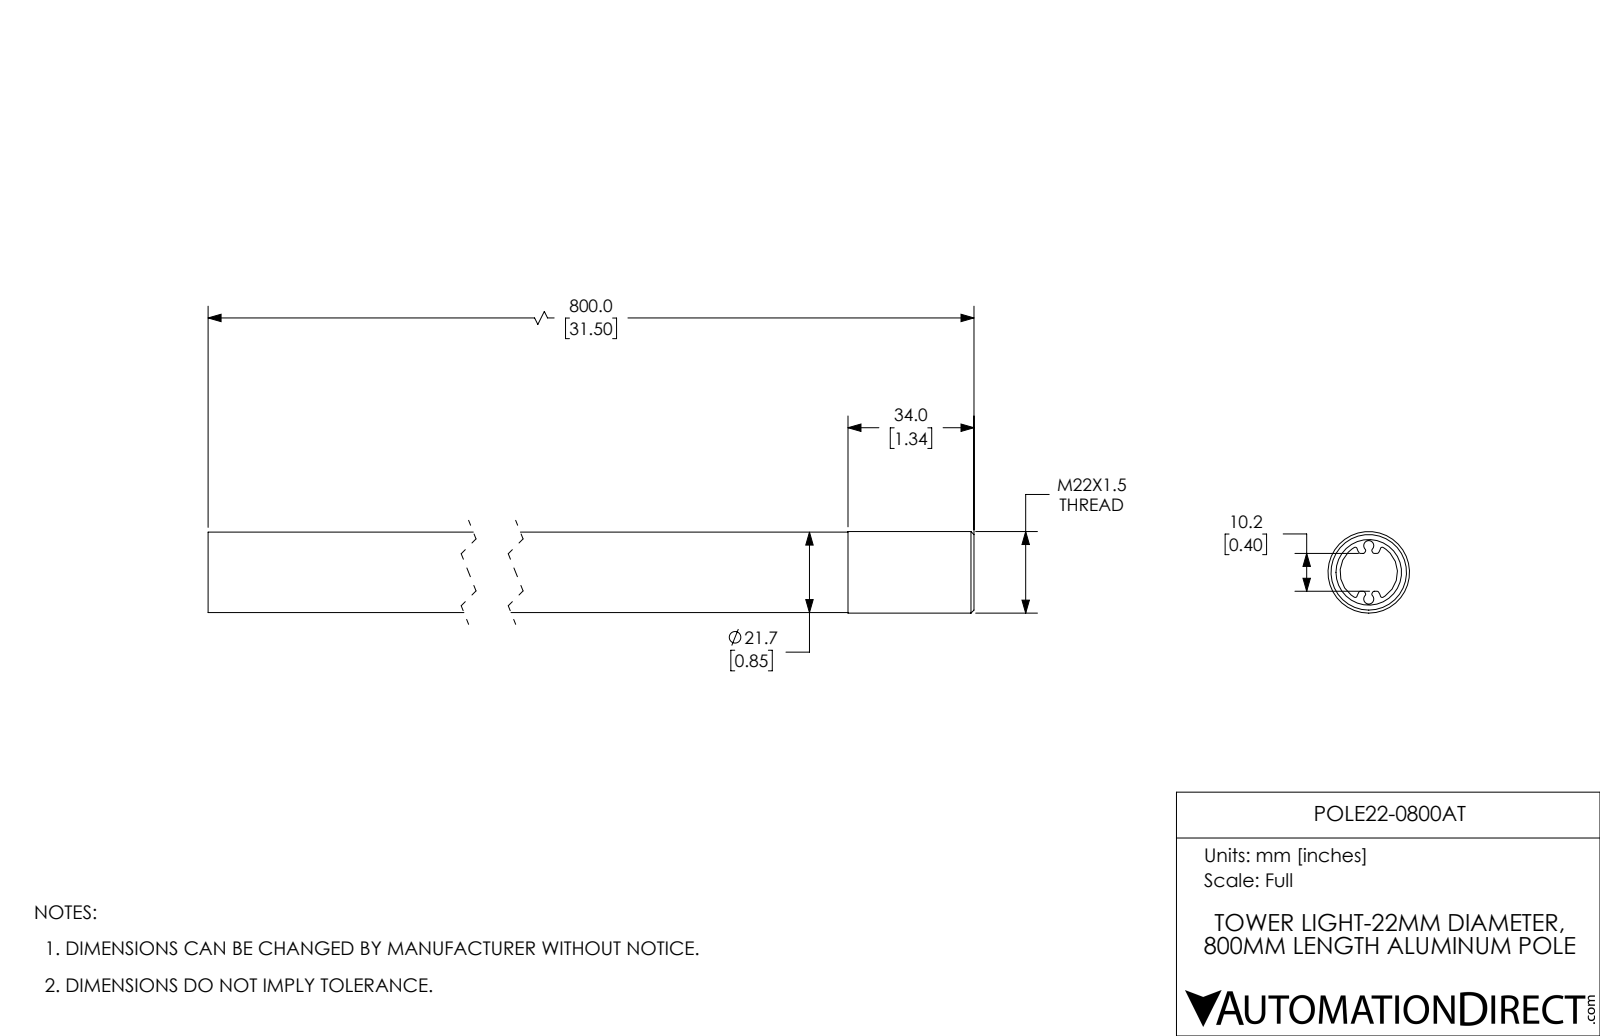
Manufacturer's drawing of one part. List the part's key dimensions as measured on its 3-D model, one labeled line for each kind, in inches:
Part name (STEP PRODUCT): POLE22-0800AT
STEP written by: SolidWorks 2017 (AUTOMOTIVE_DESIGN)
Units: inches
Bodies: 1 solid, 16 faces (4 planar, 6 cylindrical, 6 other)
Overall size (bounding box): 31.496 × 0.866 × 0.866
Volume: 9.494 in³ · Surface area: 165.1 in²
Round holes (diameter × count): ⌀0.697 ×1
Round bosses / shafts (diameter × count): ⌀0.866 ×1, ⌀0.854 ×1
Main face-to-face distances: 31.496, 0.728, 30.768, 1.339, 0.61, 30.157
